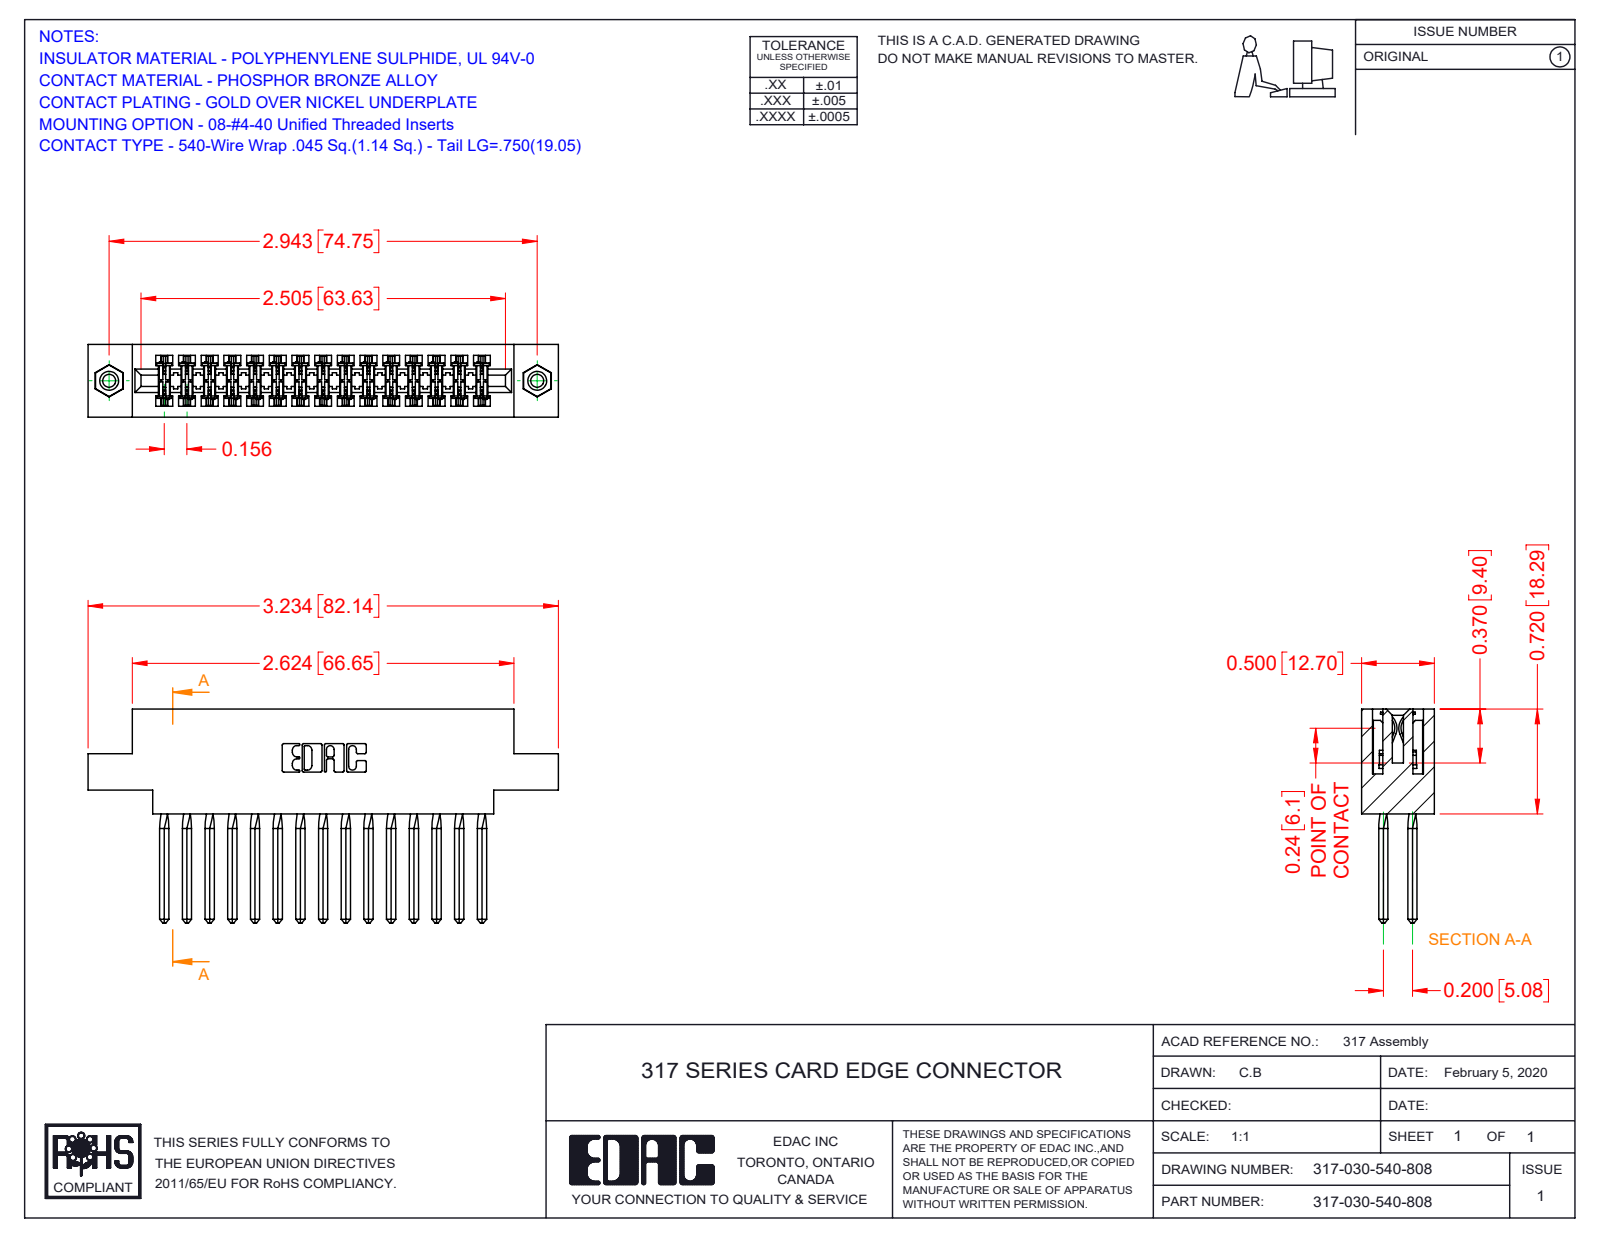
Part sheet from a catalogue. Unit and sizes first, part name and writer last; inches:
Units: inches
Overall size (bounding box): 3.234 × 1.47 × 0.5
Round holes (diameter × count): ⌀0.089 ×2, ⌀0.125 ×2, ⌀0.156 ×2
Round bosses / shafts (diameter × count): ⌀0.155 ×2
Partial cylindrical surfaces — rounded edges, fillets, slot ends (radius × count): R0.015 ×60, R0.01 ×22, R0.007 ×6, R0.031 ×6, R0.026 ×3, R0.095 ×2, R0.1 ×2, R0.11 ×2
Main face-to-face distances: 0.5, 0.075, 0.425, 0.11, 0.35, 0.22, 0.136, 0.72, 0.195, 0.116
Hole centre spacings: 2.943
Volume: 0.785 in³ · Surface area: 28.19 in²
Bodies: 33 solids, 2832 faces (2280 planar, 416 cylindrical, 136 other)
Part name (STEP PRODUCT): 345-250-001_345-250-003-102; 317-290-001_540; 317 Part_.156 Dia - TI; 317-030-540-878
STEP written by: SolidWorks 2016 (CONFIG_CONTROL_DESIGN)
